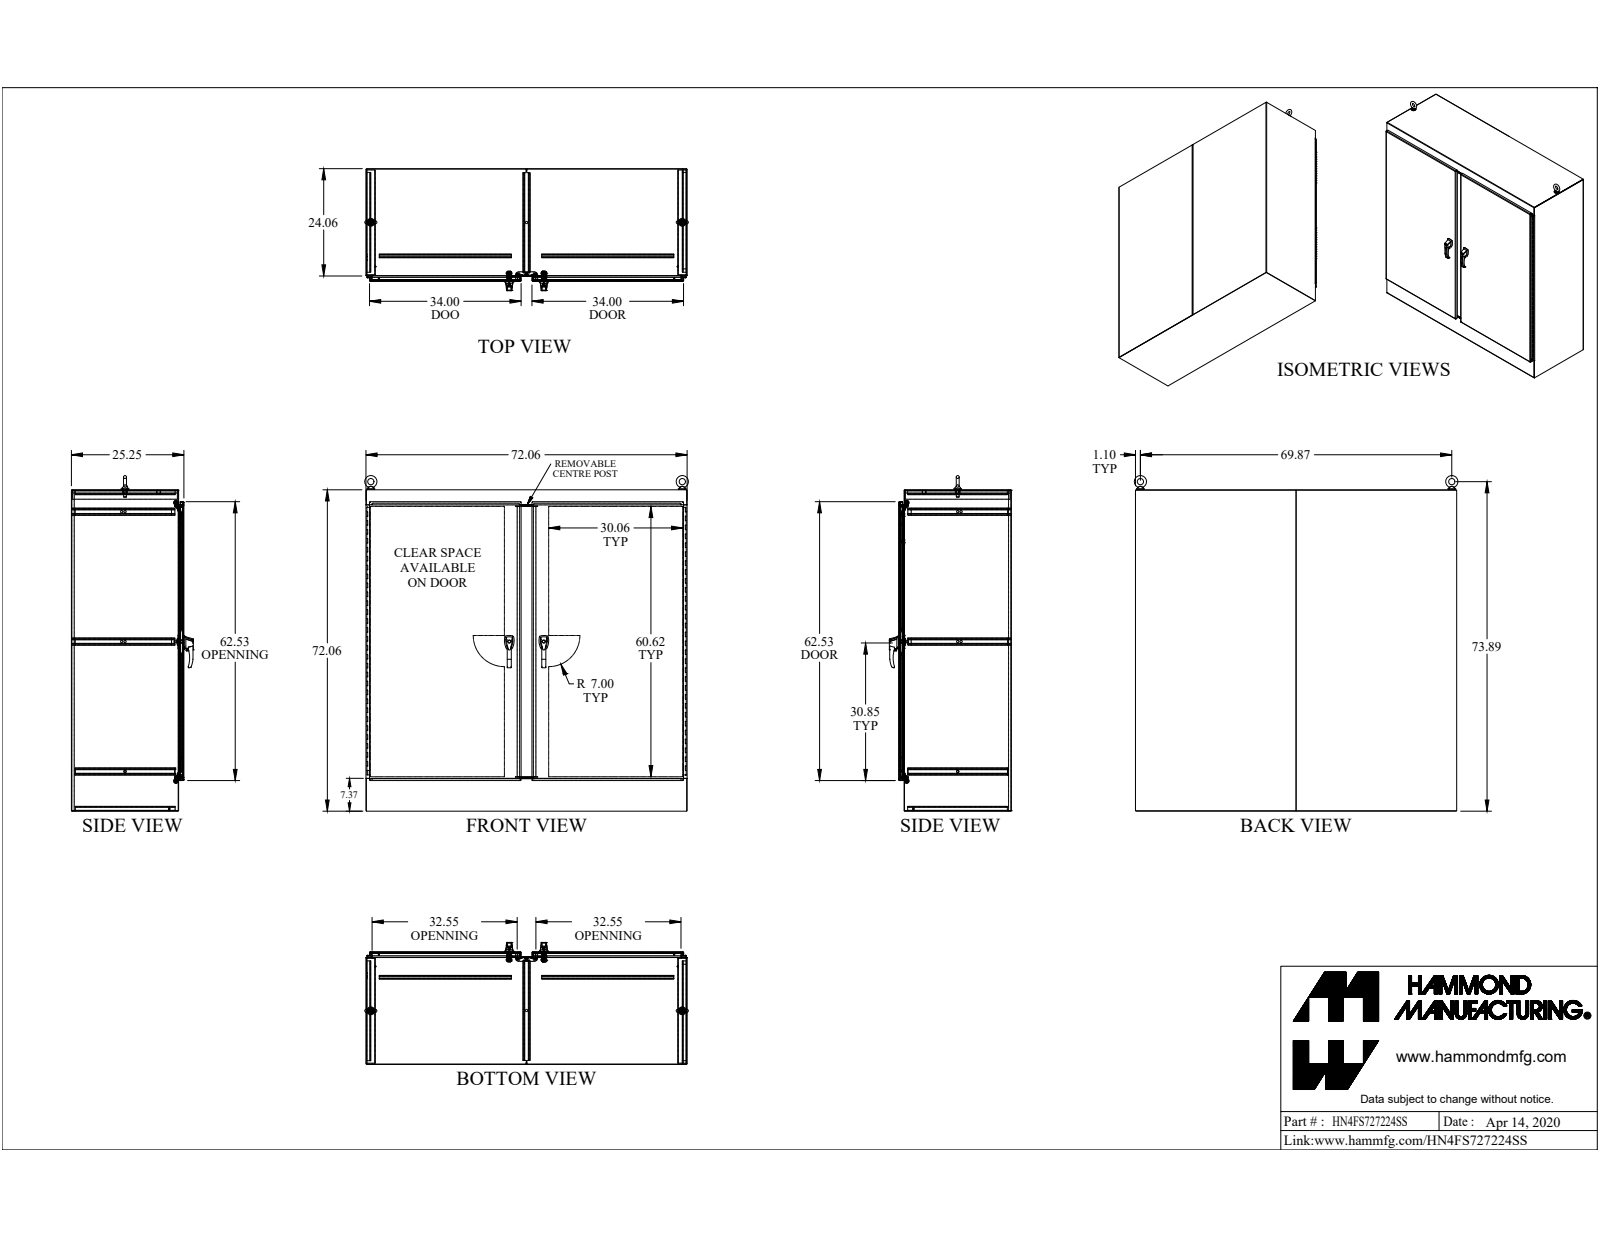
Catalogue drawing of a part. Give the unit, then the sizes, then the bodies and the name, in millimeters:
Units: millimetres
Overall size (bounding box): 1911.5 × 1844.1 × 695
Round holes (diameter × count): ⌀7.7 ×20, ⌀8.9 ×8, ⌀6.4 ×7, ⌀12.7 ×7, ⌀6.5 ×4, ⌀7.1 ×4, ⌀7.1 ×4, ⌀8 ×4, ⌀9.9 ×4, ⌀10.5 ×4, ⌀5.1 ×3, ⌀8 ×3
Round bosses / shafts (diameter × count): ⌀25.4 ×4, ⌀19.1 ×4, ⌀16 ×4, ⌀15.9 ×4, ⌀11.2 ×4, ⌀9.4 ×4, ⌀8 ×4, ⌀7.1 ×4
Partial cylindrical surfaces — rounded edges, fillets, slot ends (radius × count): R1.1 ×54, R3.5 ×48, R12.7 ×33, R2.5 ×28, R3.2 ×27, R0.5 ×24, R1.5 ×24, R8.1 ×19
Main face-to-face distances: 2.4, 638.9, 1827.9, 636.4, 641.3, 1825.5, 1830.3, 30.1, 608.7, 32.6
Hole centre spacings: 152.4, 1792.8, 304.8, 1812.2, 457.2, 1843.9, 609.6, 1887.5
Volume: 32 200 000 mm³ · Surface area: 26 770 000 mm²
Bodies: 106 solids, 2965 faces (1563 planar, 1156 cylindrical, 246 other)
Part name (STEP PRODUCT): HN4FS727224SS
STEP written by: SolidWorks 2019 (CONFIG_CONTROL_DESIGN)
